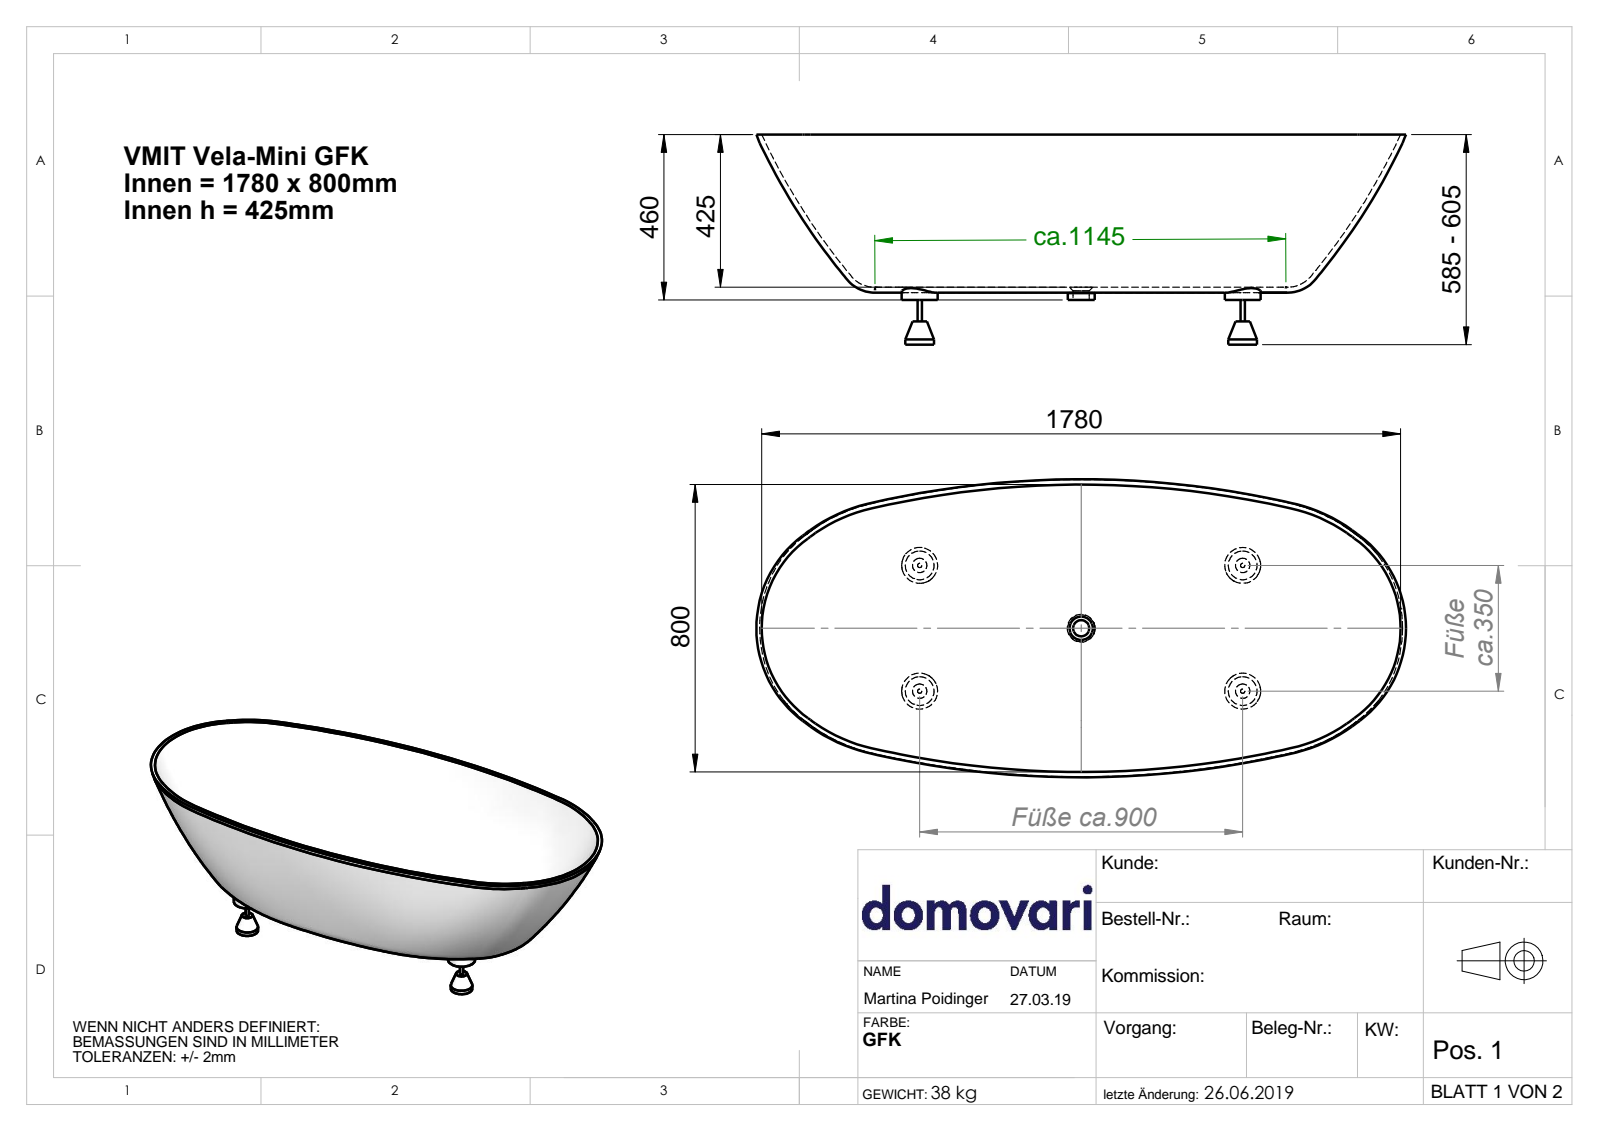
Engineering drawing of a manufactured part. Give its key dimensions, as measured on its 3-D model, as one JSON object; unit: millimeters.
{"part_name": "VMIT", "step_written_by": "SolidWorks 2019 (AUTOMOTIVE_DESIGN)", "units": "millimeters", "bodies": {"solids": 2, "faces": 122, "planar": 26, "cylindrical": 24, "other": 72}, "overall_size": [1820, 840, 585], "volume_mm3": 52030000, "surface_area_mm2": 5212000, "round_bosses_or_shafts": [[100, 4], [80, 4], [12, 4]], "face_to_face_distances": [10, 810, 450, 460, 125, 575, 585, 820, 800, 1790]}
